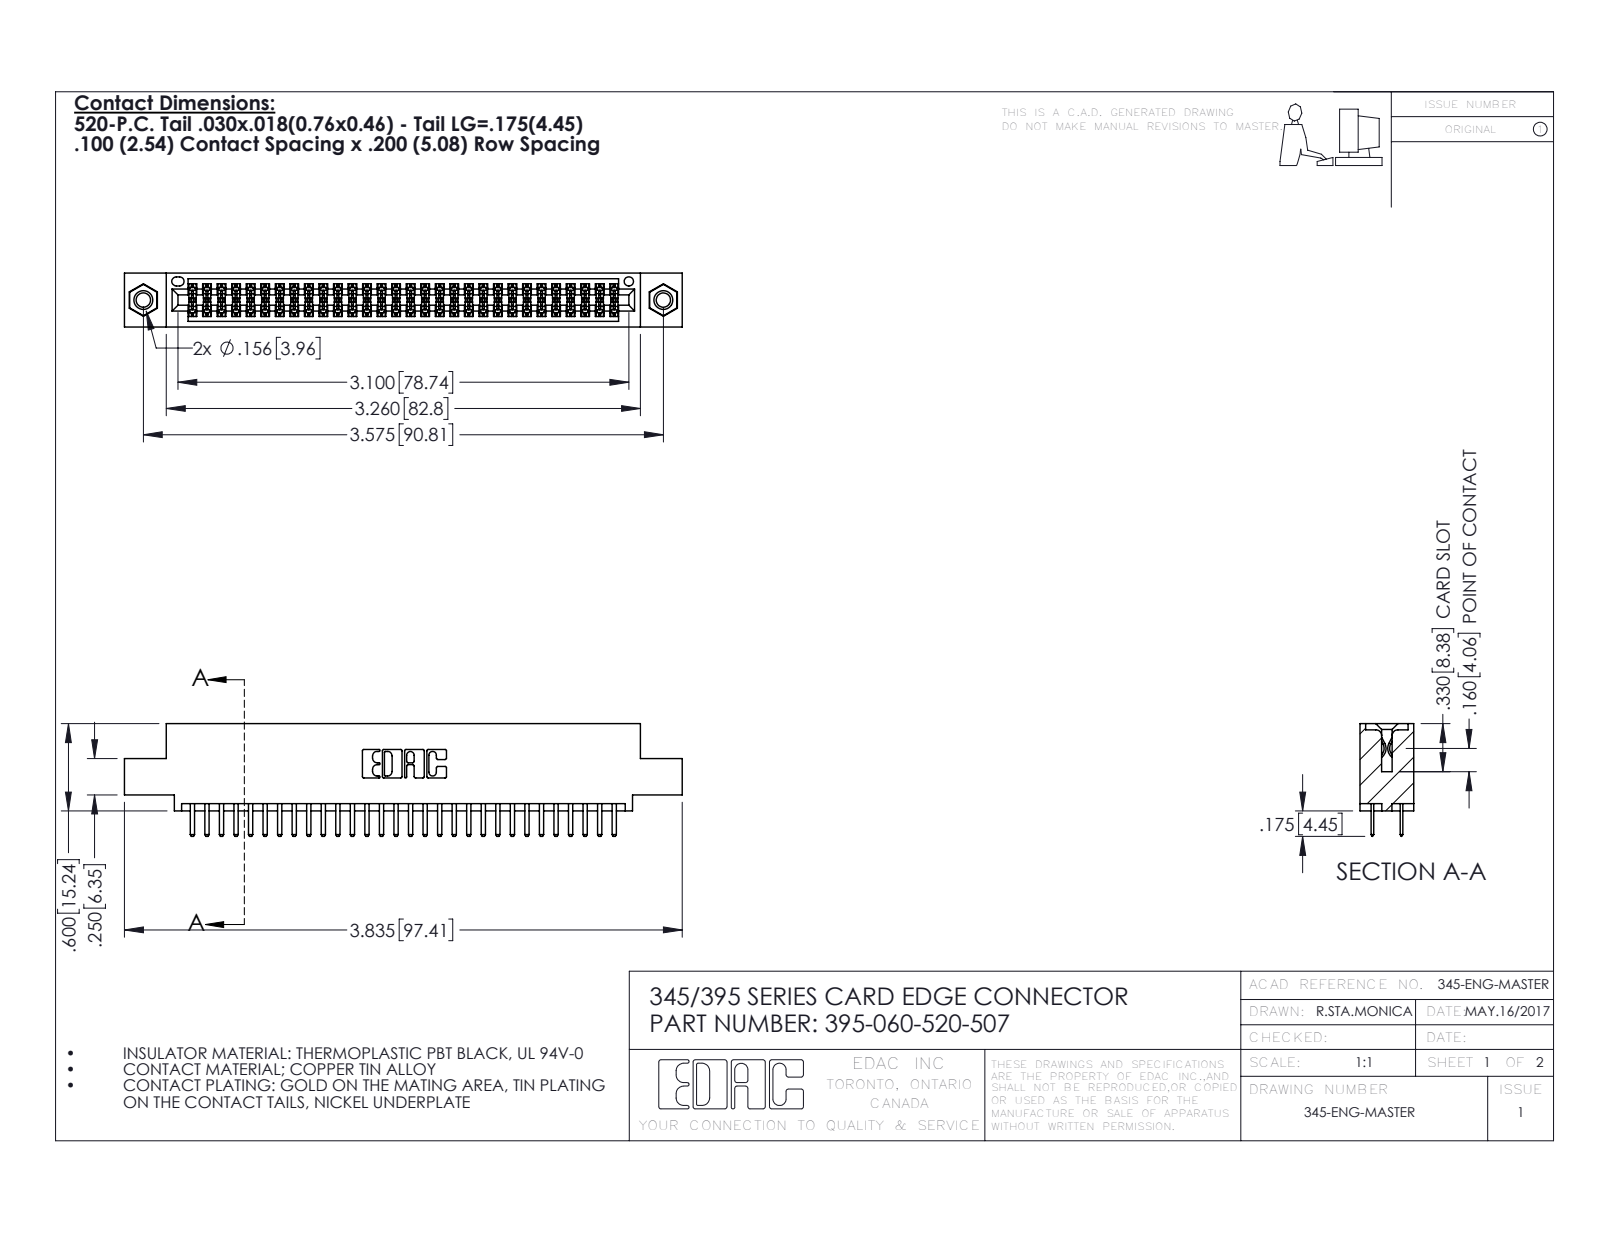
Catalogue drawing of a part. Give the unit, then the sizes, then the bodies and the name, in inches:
Units: inches
Overall size (bounding box): 3.835 × 0.775 × 0.37
Round holes (diameter × count): ⌀0.098 ×2, ⌀0.125 ×2, ⌀0.156 ×2, ⌀0.064 ×1
Round bosses / shafts (diameter × count): ⌀0.155 ×2
Partial cylindrical surfaces — rounded edges, fillets, slot ends (radius × count): R0.006 ×90, R0.01 ×64, R0.01 ×22, R0.007 ×6, R0.031 ×6, R0.026 ×3, R0.014 ×2, R0.019 ×2
Main face-to-face distances: 0.072, 0.298, 0.2, 0.37, 0.098, 0.272, 0.025, 0.225, 0.022, 0.072
Hole centre spacings: 0.27, 3.34, 3.575
Volume: 0.564 in³ · Surface area: 20.91 in²
Bodies: 63 solids, 3430 faces (2216 planar, 1198 cylindrical, 16 other)
Part name (STEP PRODUCT): 345-250-001_345-250-005-103; 345-292-001_345-293-120; 395-060-520-507; 345 Part_0.110 Offset - 0.156 Dia-TI
STEP written by: SolidWorks 2016 (CONFIG_CONTROL_DESIGN)
